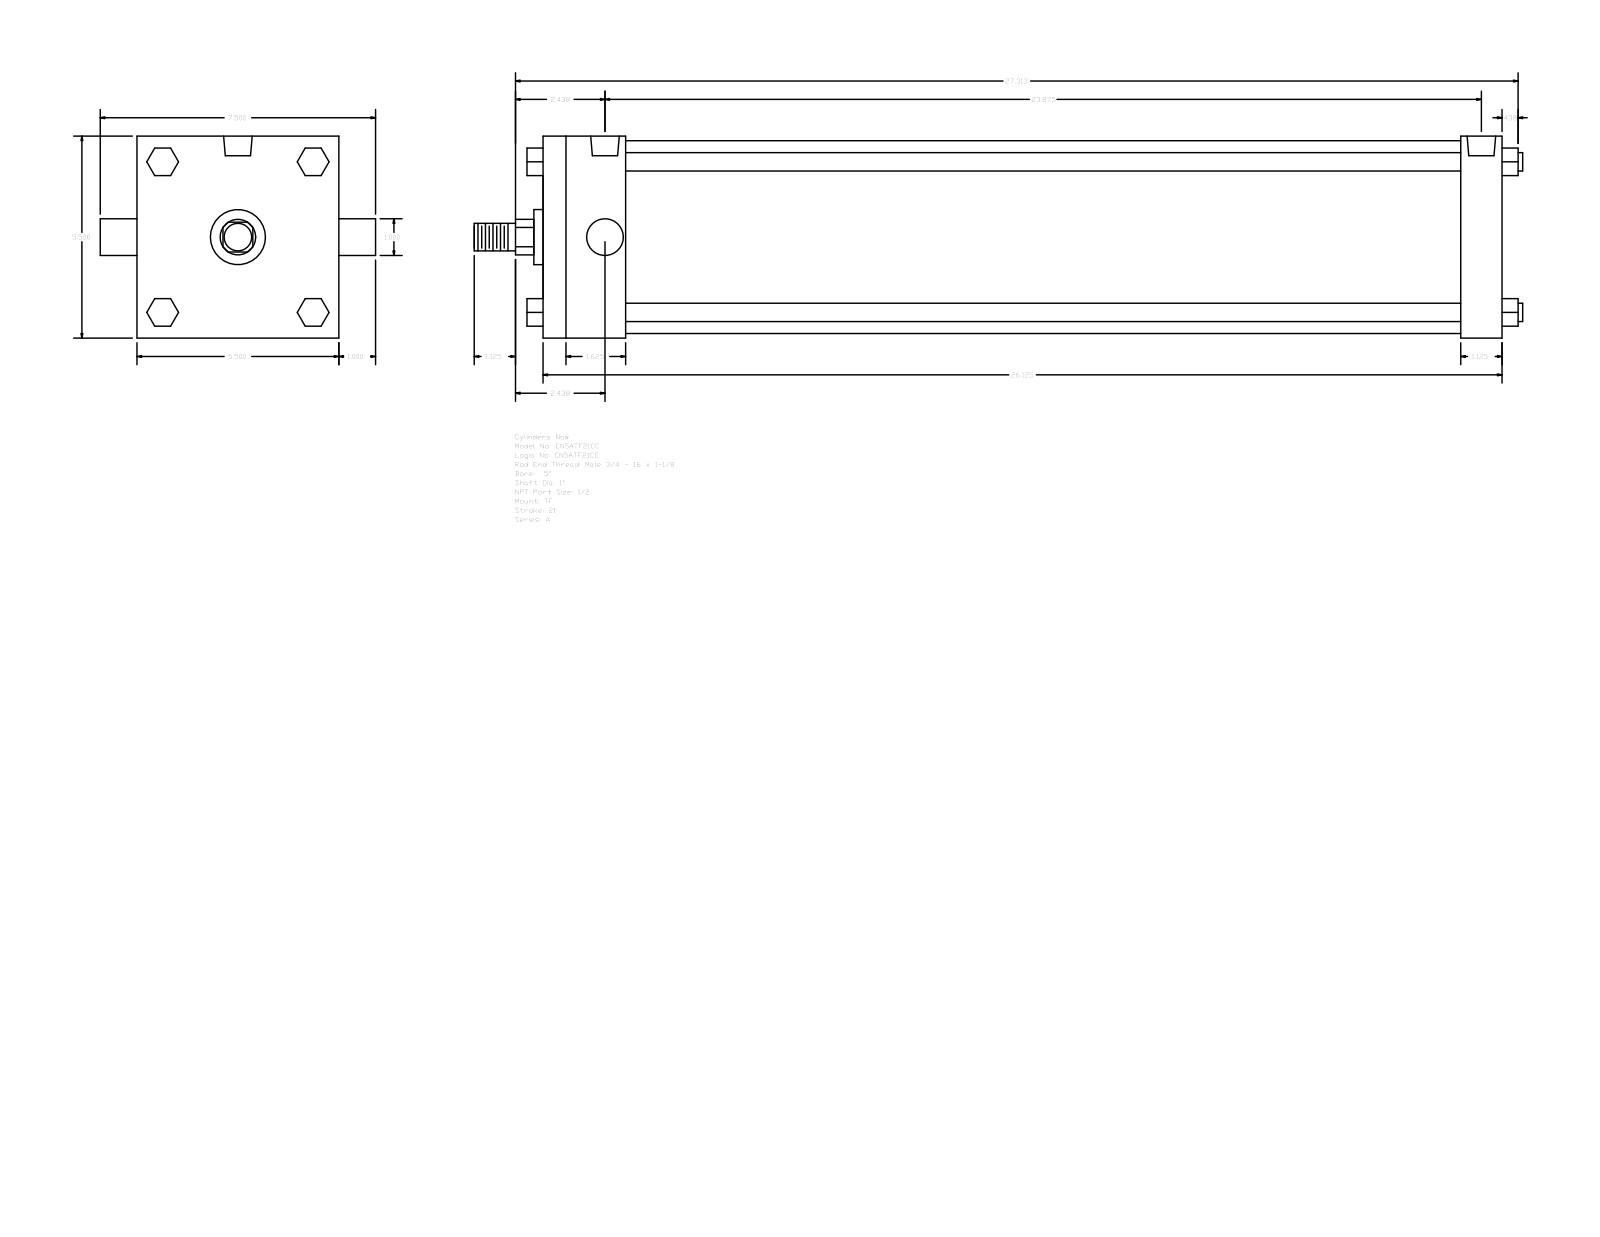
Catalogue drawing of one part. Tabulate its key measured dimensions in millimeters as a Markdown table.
| quantity | value |
| --- | --- |
| part name | A_TF__0500_1 |
| STEP written by | GSSL Pune (CONFIG_CONTROL_DESIGN) |
| units | millimeters |
| bodies | 0 solids, 120 faces (92 planar, 28 cylindrical, 0 other) |
| overall size | 725.49 × 190.5 × 139.7 |
| round holes (diameter × count) | 8.73 × 3, 19.77 × 2 |
| round bosses / shafts (diameter × count) | 12.7 × 4, 25.4 × 2, 133.35 × 1, 38.1 × 1, 19.05 × 1 |
| partial cylindrical surfaces (radius × count) | 12.29 × 1 |
| main face-to-face distances | 139.7, 663.57, 28.57, 635, 57.15, 577.85, 606.42, 19.05, 52.07, 90.18 |
| hole center spacings | 2.39, 604.04, 601.65, 606.43 |
